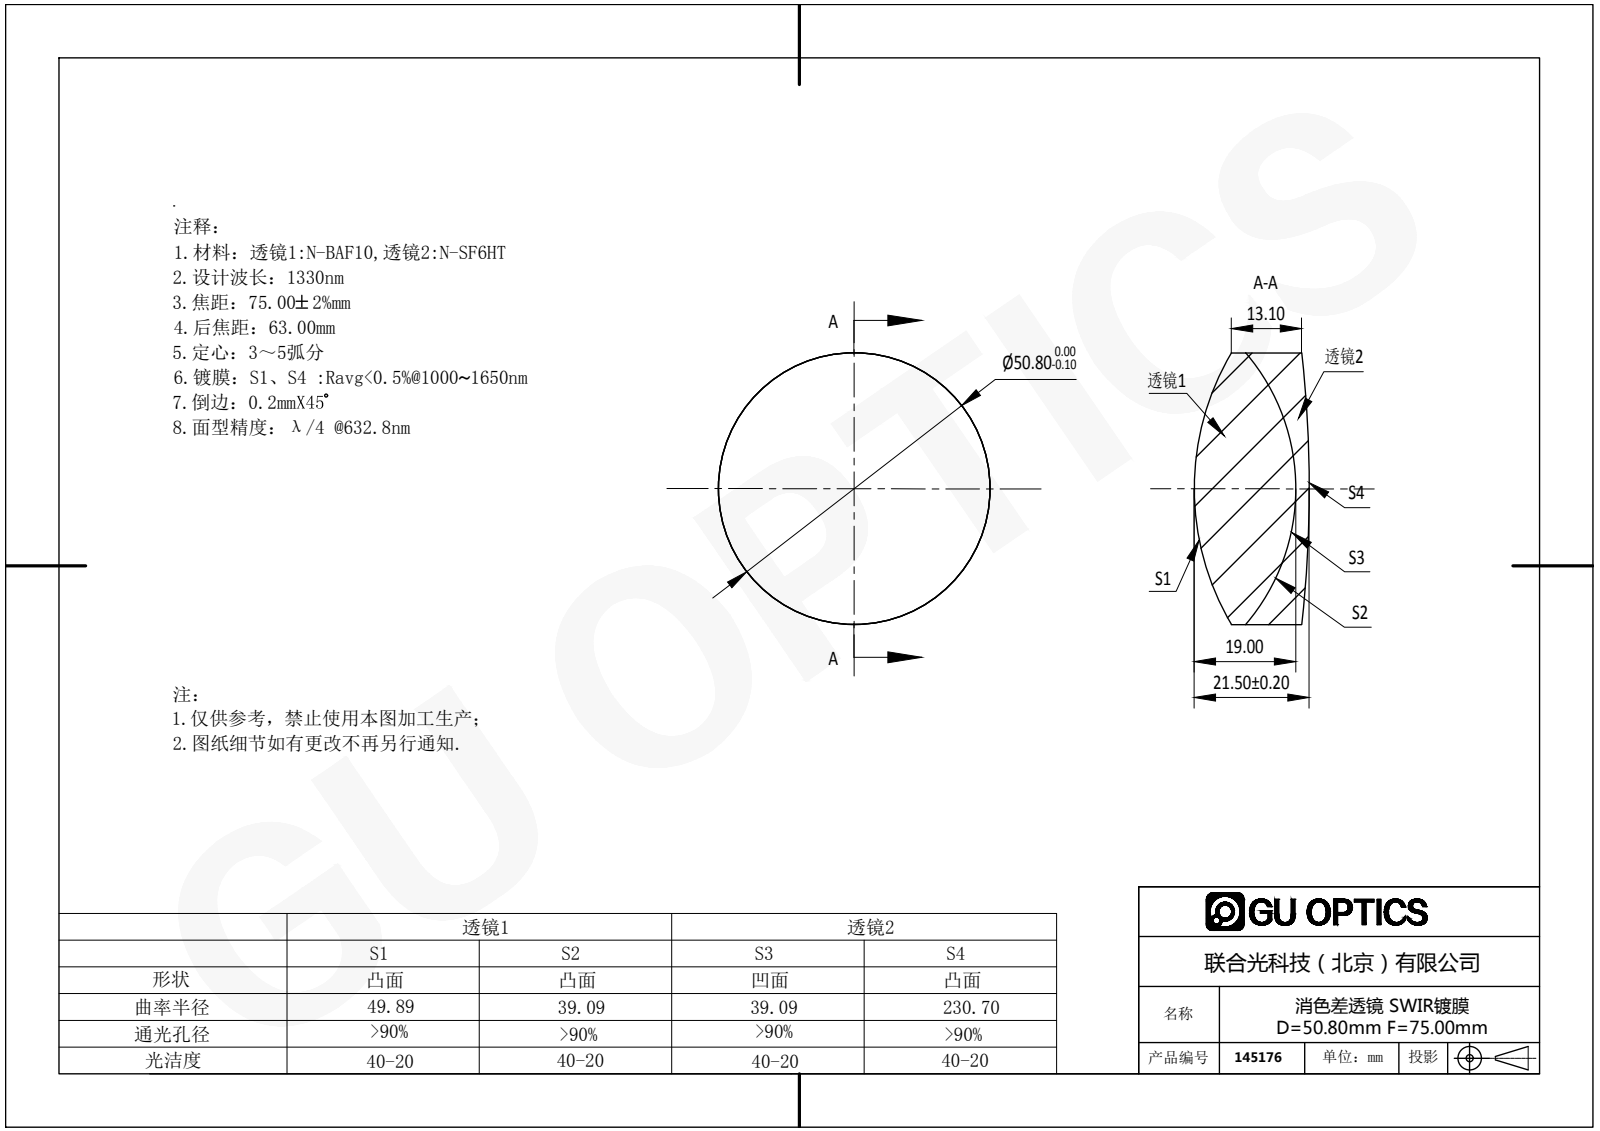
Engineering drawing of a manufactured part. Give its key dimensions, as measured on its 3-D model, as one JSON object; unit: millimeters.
{"part_name": "145176", "step_written_by": "SolidWorks 2016 (AUTOMOTIVE_DESIGN)", "units": "millimeters", "bodies": {"solids": 2, "faces": 12, "planar": 0, "cylindrical": 4, "other": 8}, "overall_size": [50.8, 50.8, 21.5], "volume_mm3": 35290, "surface_area_mm2": 10916, "round_bosses_or_shafts": [[50.8, 1]]}
